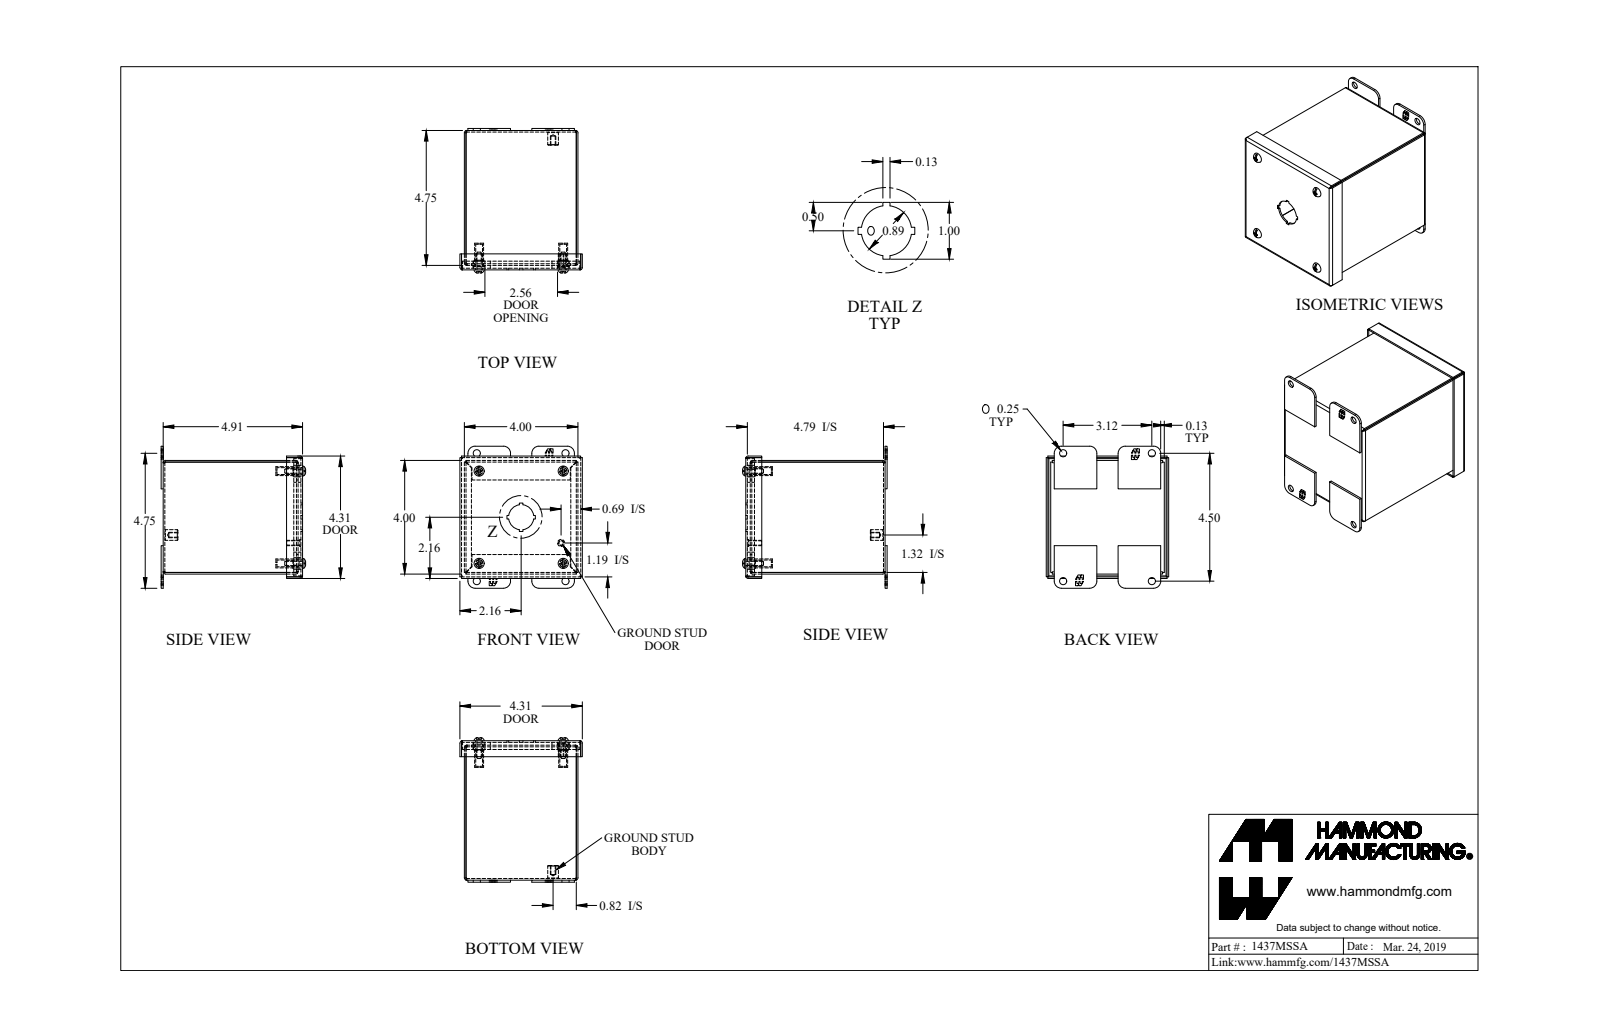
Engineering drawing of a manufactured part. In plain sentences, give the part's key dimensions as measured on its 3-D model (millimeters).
The part is named "1437MSSA". Its 3-D file was written by "SolidWorks 2019 (AUTOMOTIVE_DESIGN)". It is 21 solids with 478 faces: 371 planar, 88 cylindrical and 19 other. Overall it measures 129.3 by 127 by 109.5 millimeters. Its volume is 151 900 cubic millimeters and its surface area 190 800 square millimeters. Round holes: 8 of diameter 6.4, 4 of diameter 1.7, 4 of diameter 6.1, 4 of diameter 6.4, 4 of diameter 10.3, 1 of diameter 4, 1 of diameter 22.5. Round bosses or shafts: 5 of diameter 4.8, 4 of diameter 10.3, 4 of diameter 8, 4 of diameter 3.8, 1 of diameter 9.5, 1 of diameter 6.4. Partial cylindrical surfaces (rounded edges, fillets, slot ends): 12 of radius 0.7, 12 of radius 2.2, 8 of radius 6.4, 4 of radius 4.3, 2 of radius 3.2. The main face-to-face distances are 1.4, 100.2, 123.2, 98.7, 101.6, 124.6, 4, 104.1, 121.7, 4. The hole center spacings are 82.6, 16, 75.2, 78.9, 98.5, 111.7, 125.1, 75.2.
